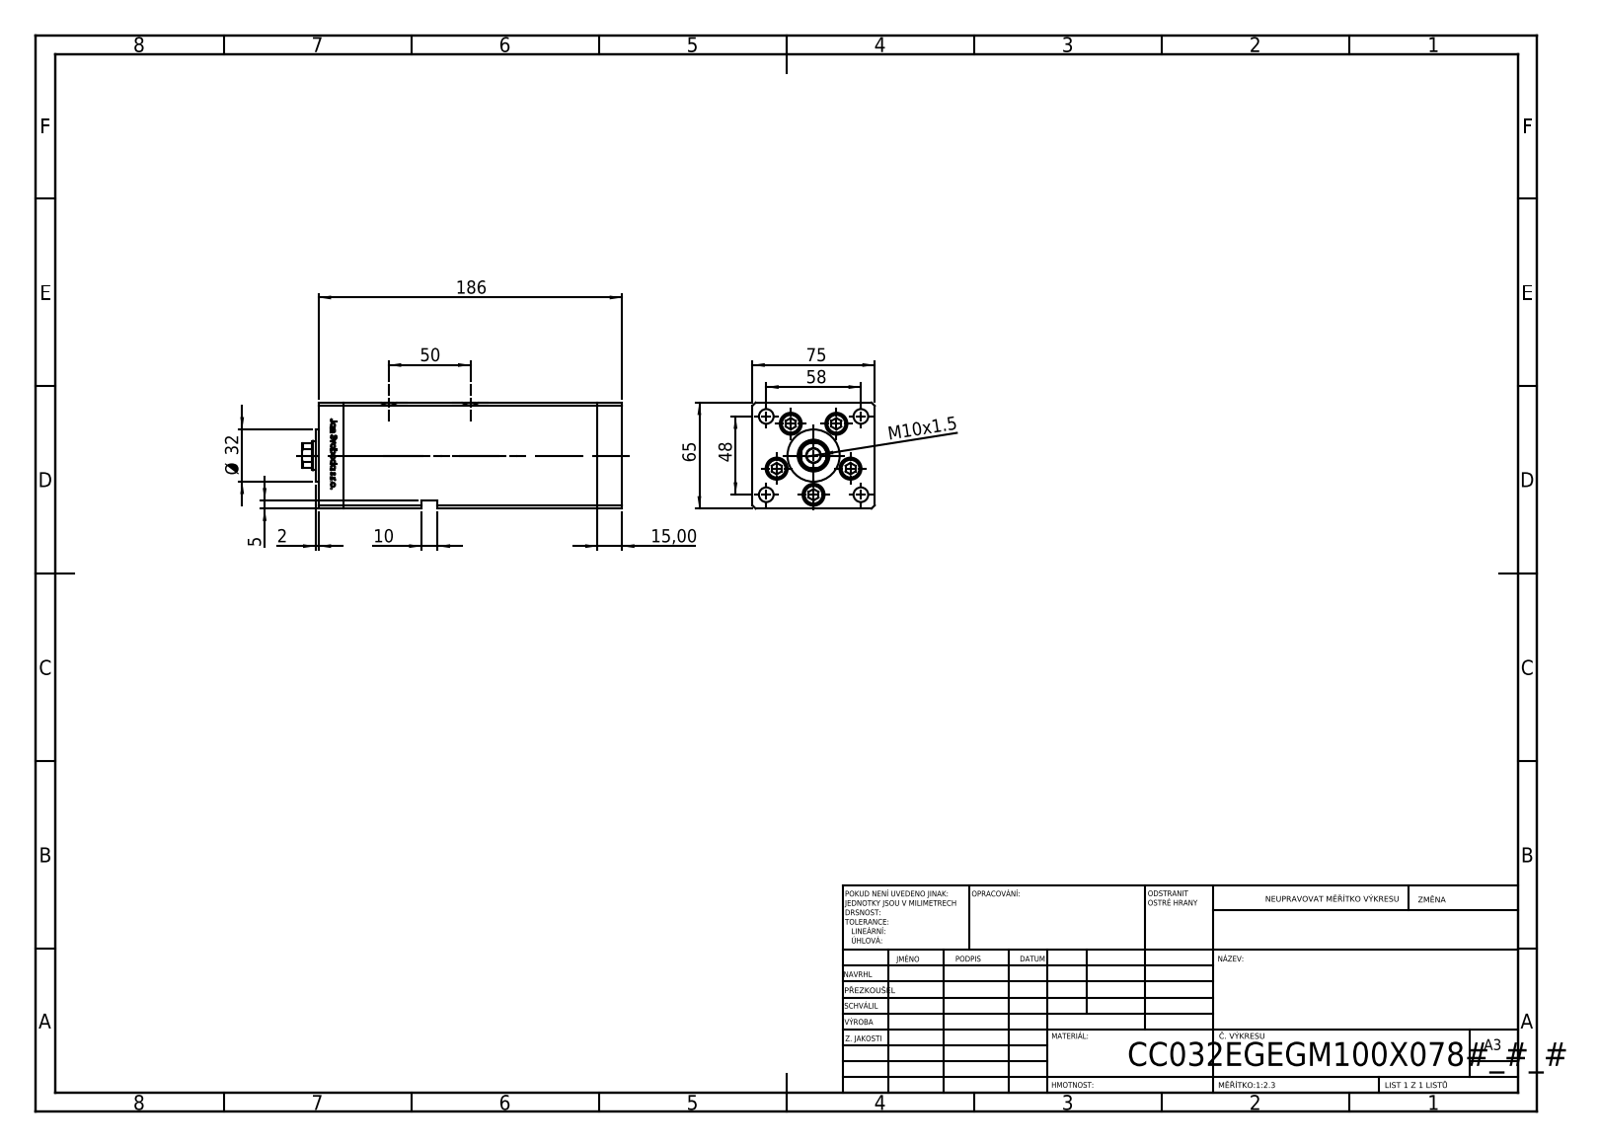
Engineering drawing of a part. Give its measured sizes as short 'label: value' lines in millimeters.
name: V220C_E MIDDLE; V220C_FRONT_E; V220C_VC_E; ALLEN BOLT (+1 more)
written by: SolidWorks 2019 (CONFIG_CONTROL_DESIGN)
unit: mm
bodies: 14 solids, 1212 faces (473 planar, 165 cylindrical, 574 other)
size: 196 × 75 × 65
volume: 769 603 mm³; area: 146 638 mm²
holes: 9× ⌀9, 5× ⌀13.5, 4× ⌀10.5, 4× ⌀16.5, 2× ⌀2, 2× ⌀13.16, 1× ⌀8.5, 1× ⌀18, 1× ⌀19.5
bosses: 5× ⌀12.5, 5× ⌀8, 1× ⌀32
rounds: 2× R0.93, 1× R8.5
face distances: 75, 65, 15, 156, 171, 186, 28, 54.5, 10.5, 26.25
hole spacings: 24, 37.64, 58, 15.67, 17.22, 27.71, 28.83, 29
